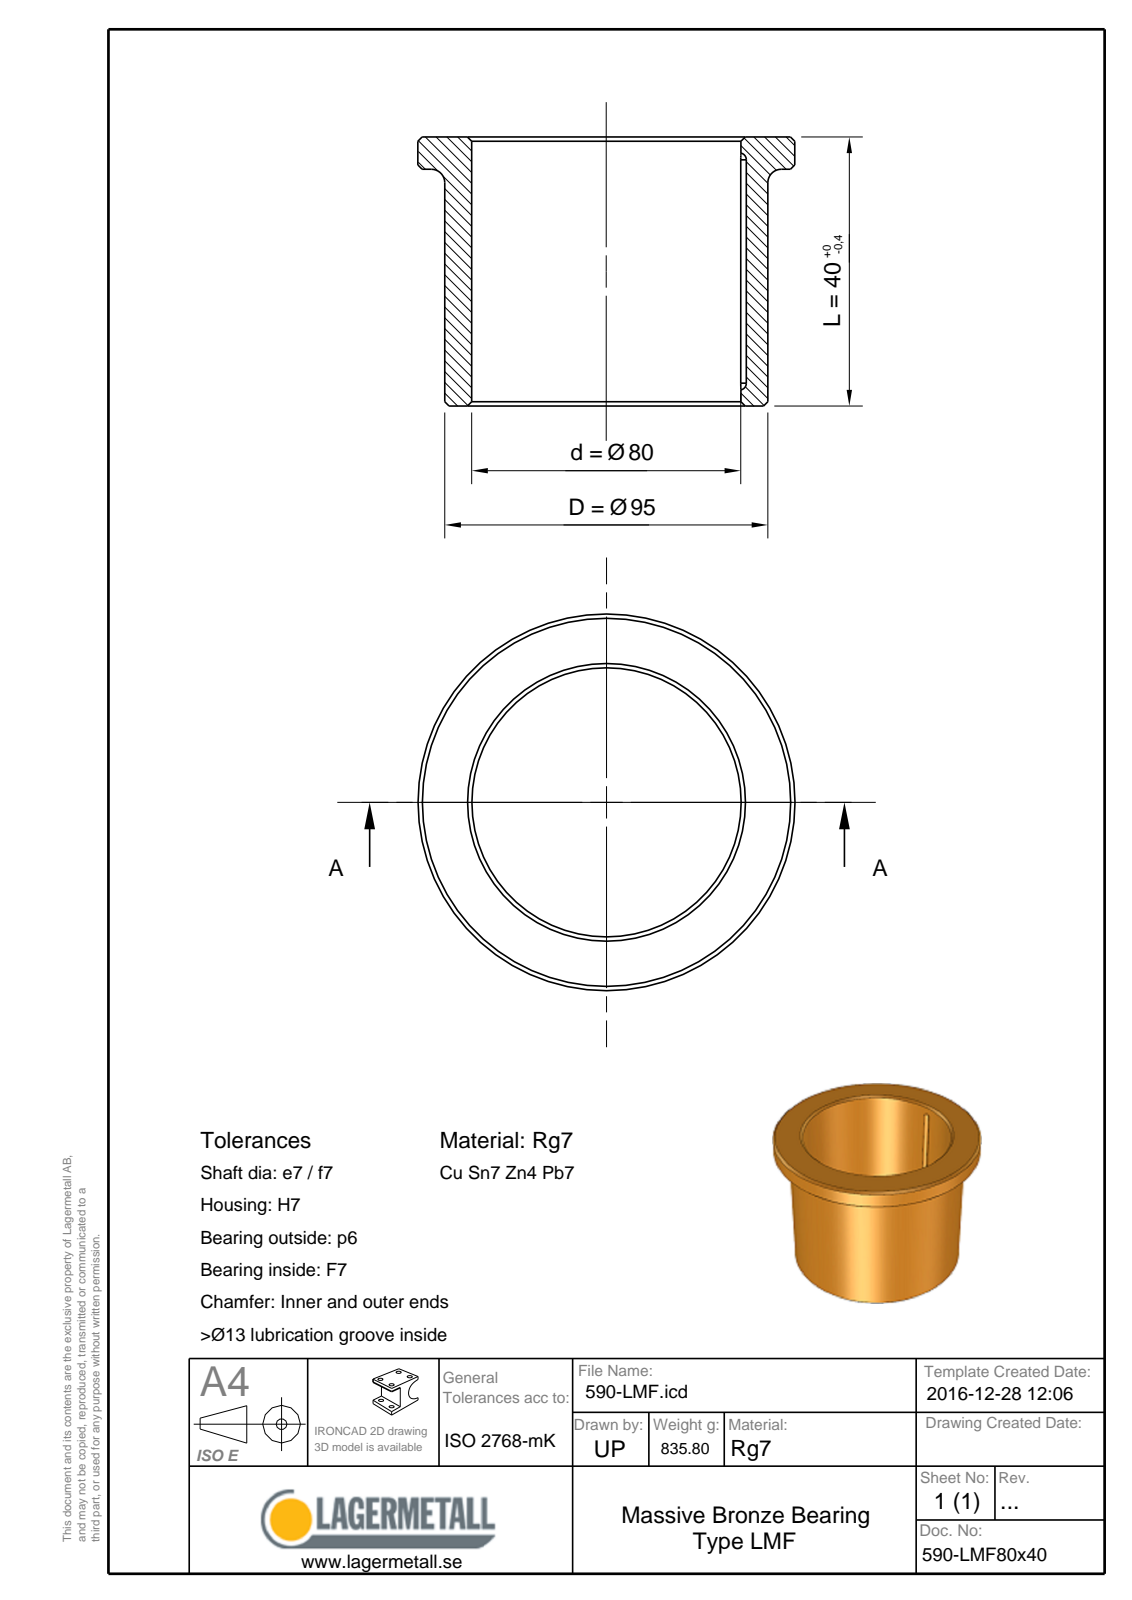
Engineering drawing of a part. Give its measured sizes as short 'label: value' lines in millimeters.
name: 590-LMF80x40
written by: Spatial InterOp 3D (CONFIG_CONTROL_DESIGN)
unit: mm
bodies: 1 solid, 17 faces (4 planar, 5 cylindrical, 8 other)
size: 105 × 105 × 40
volume: 94 979 mm³; area: 28 260 mm²
holes: 1× ⌀80
bosses: 1× ⌀105, 1× ⌀95
rounds: 2× R1.75
face distances: 40, 32, 8
